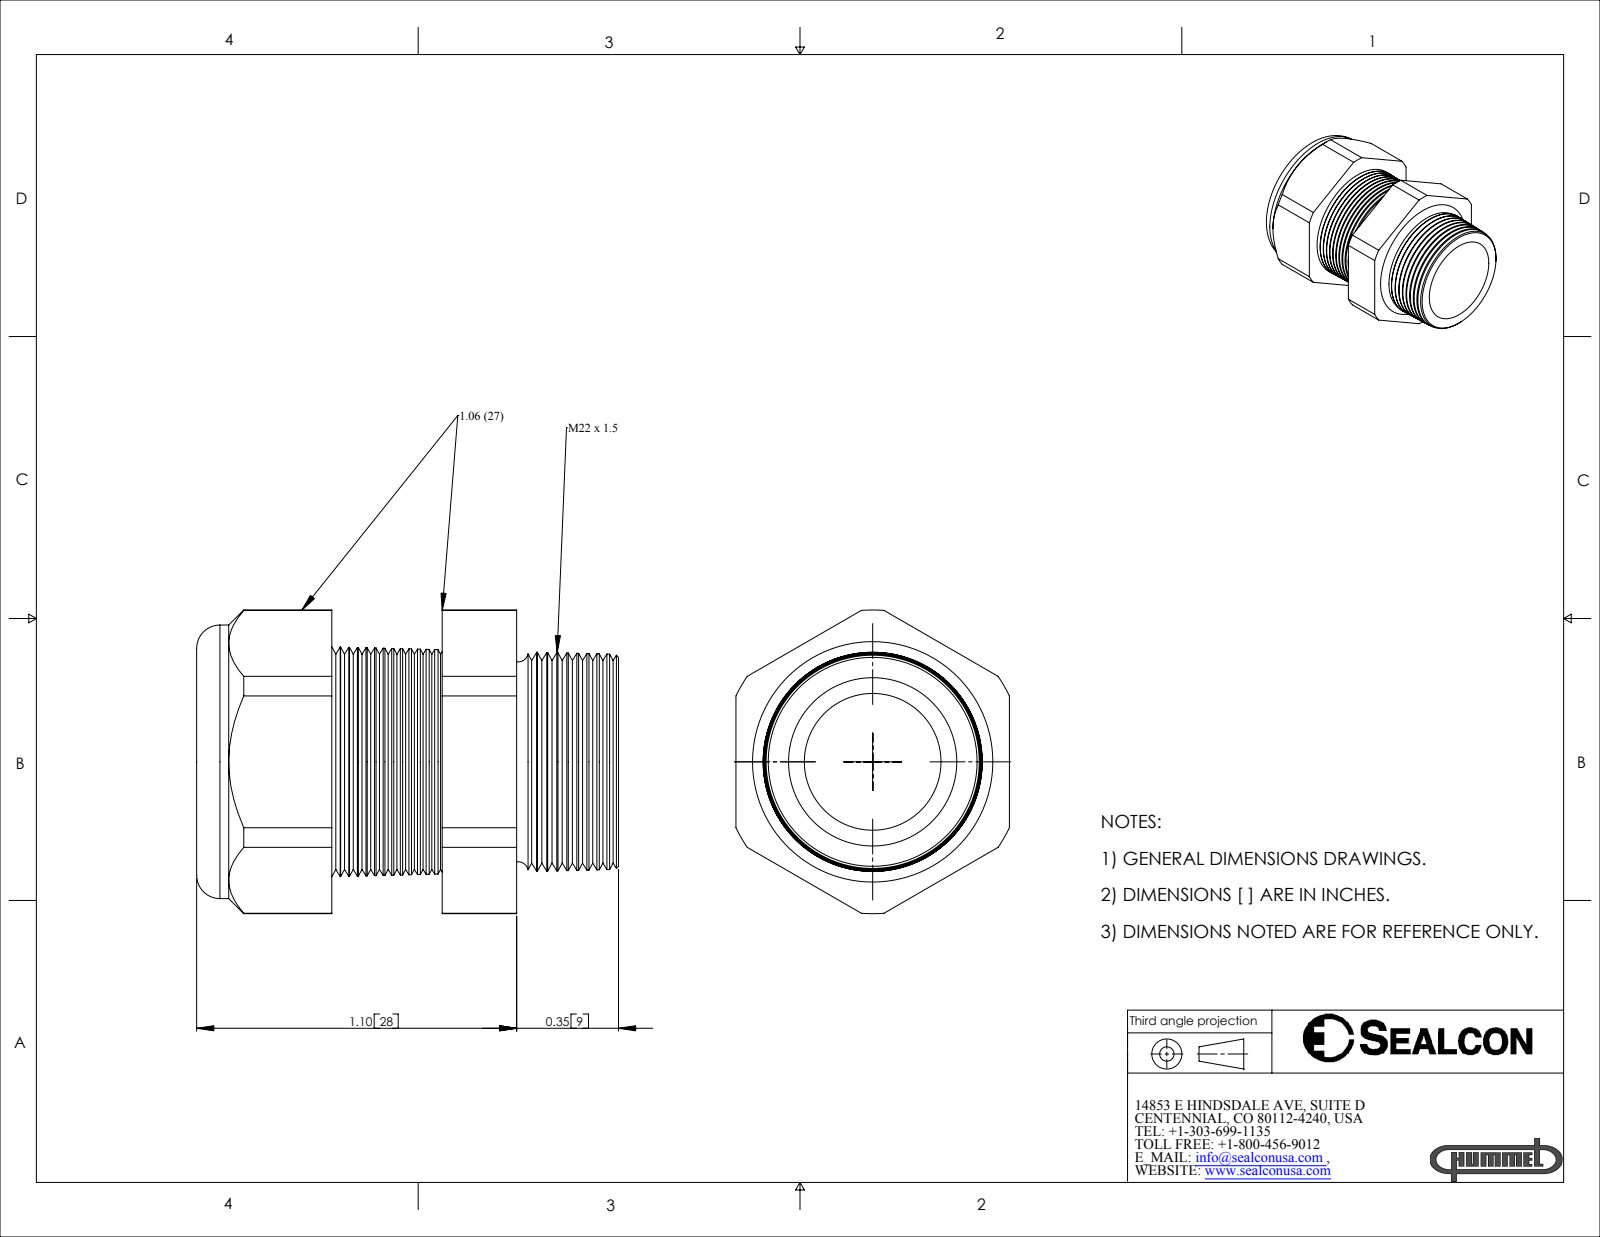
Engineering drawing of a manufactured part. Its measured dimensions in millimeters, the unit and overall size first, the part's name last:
Units: millimetres
Overall size (bounding box): 36.8 × 26.5 × 23.9
Round holes (diameter × count): ⌀11.4 ×1, ⌀11.9 ×1
Round bosses / shafts (diameter × count): ⌀23.9 ×1
Partial cylindrical surfaces — rounded edges, fillets, slot ends (radius × count): R13.3 ×1
Main face-to-face distances: 23.9, 21.4, 11.8, 9.7, 27.9, 16.1, 6.5, 6.4, 5.5, 15.1
Volume: 9 750 mm³ · Surface area: 6 465 mm²
Bodies: 2 solids, 186 faces (20 planar, 20 cylindrical, 146 other)
Part name (STEP PRODUCT): CD22MP-GY
STEP written by: SolidWorks 2007 (CONFIG_CONTROL_DESIGN)
